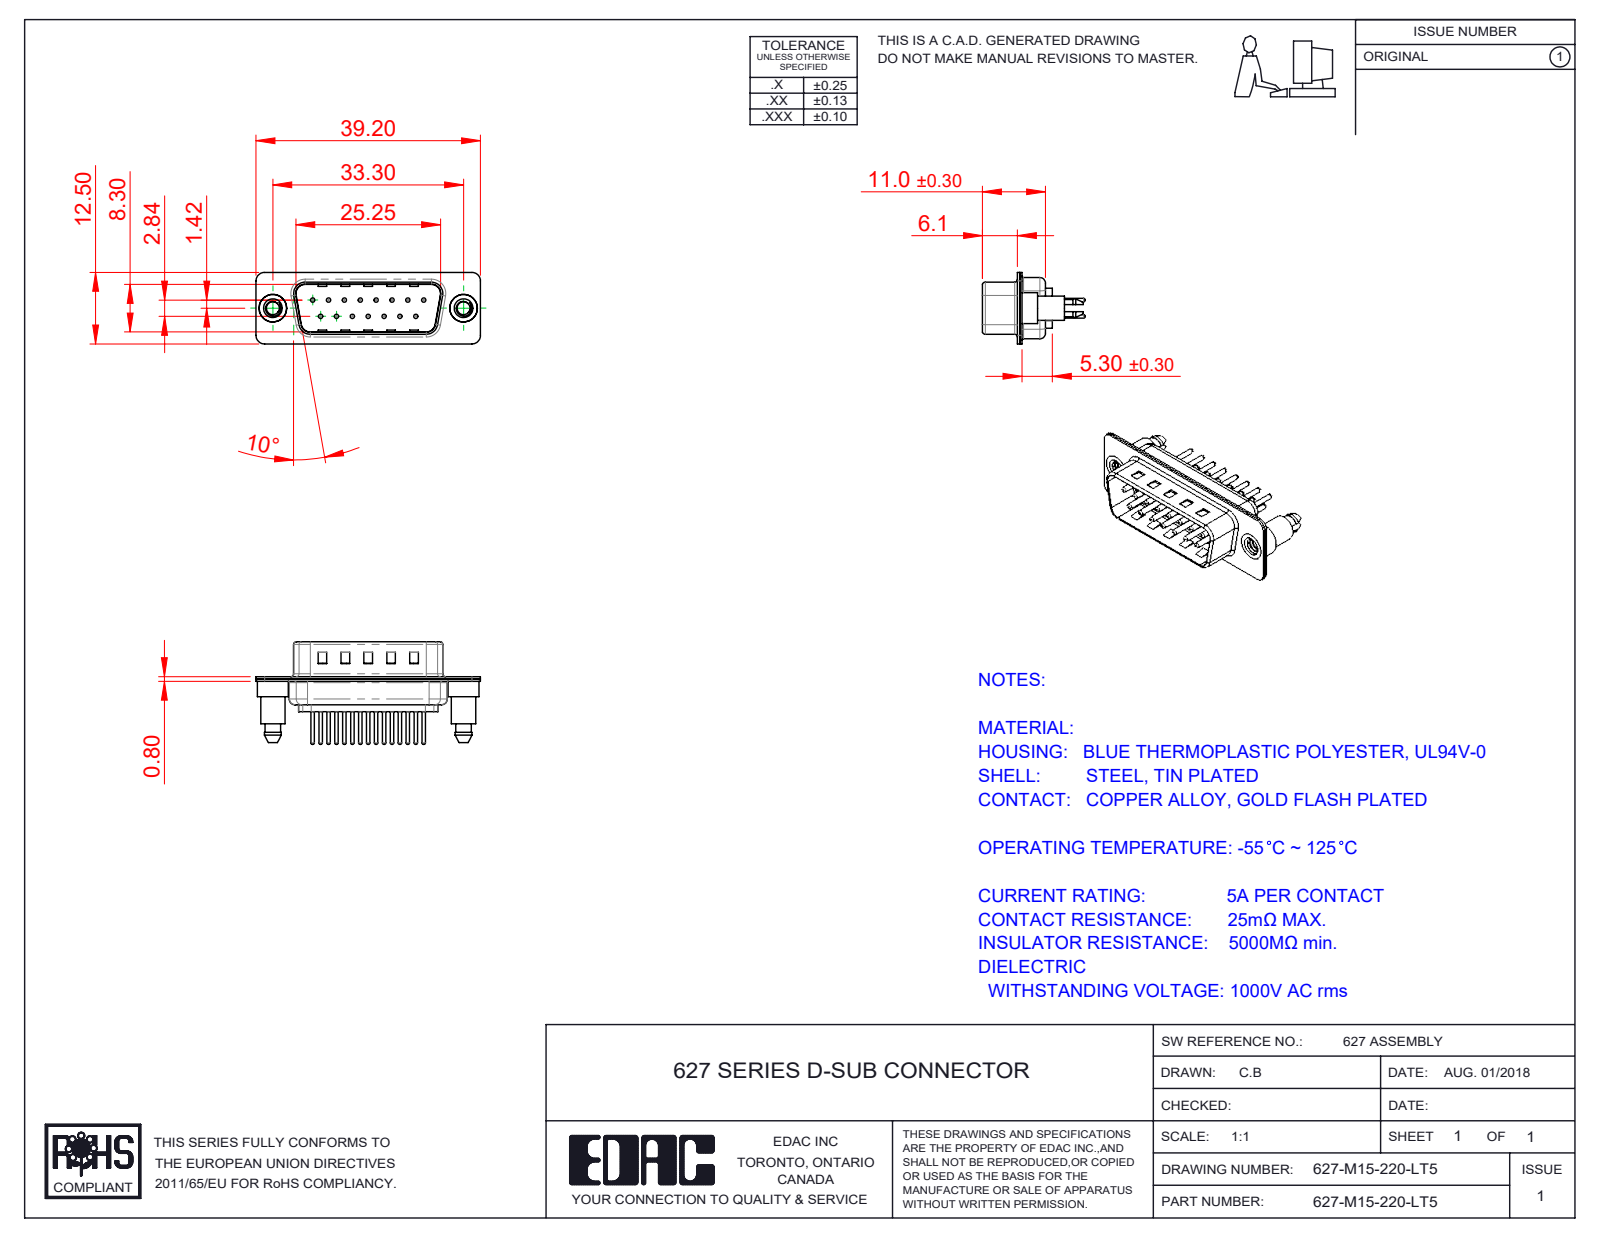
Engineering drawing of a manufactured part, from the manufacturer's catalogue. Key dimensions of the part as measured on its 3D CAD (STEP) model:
Part name (STEP PRODUCT): 627M Housing_15 Contacts; 627M Shell Rear_15 Contacts; 627M Contact Row 2_20; 627M 4-40 Threaded Boardlock (+3 more)
STEP written by: SolidWorks 2020 (CONFIG_CONTROL_DESIGN)
Units: millimetres
Bodies: 20 solids, 945 faces (260 planar, 375 cylindrical, 310 other)
Overall size (bounding box): 39.2 × 17.9 × 12.5
Volume: 1 977 mm³ · Surface area: 5 141 mm²
Round holes (diameter × count): ⌀0.75 ×15, ⌀1.6 ×15, ⌀2 ×15, ⌀2.26 ×2, ⌀4 ×2, ⌀4.8 ×2
Round bosses / shafts (diameter × count): ⌀1.5 ×15, ⌀0.6 ×15, ⌀5.4 ×2, ⌀4.9 ×2, ⌀4.25 ×2
Partial cylindrical surfaces — rounded edges, fillets, slot ends (radius × count): R1.5 ×18, R2 ×12, R1.6 ×10, R0.5 ×8, R0.25 ×4, R0.6 ×4, R0.65 ×4, R0.9 ×4
Main face-to-face distances: 0.4, 0.8, 9.5, 9.1, 8.7, 9.9, 5.3, 1.2, 6.1, 5.7
Hole centre spacings: 3.16, 2.77, 5.54, 8.31, 11.08, 5.03, 5.04, 7.48
